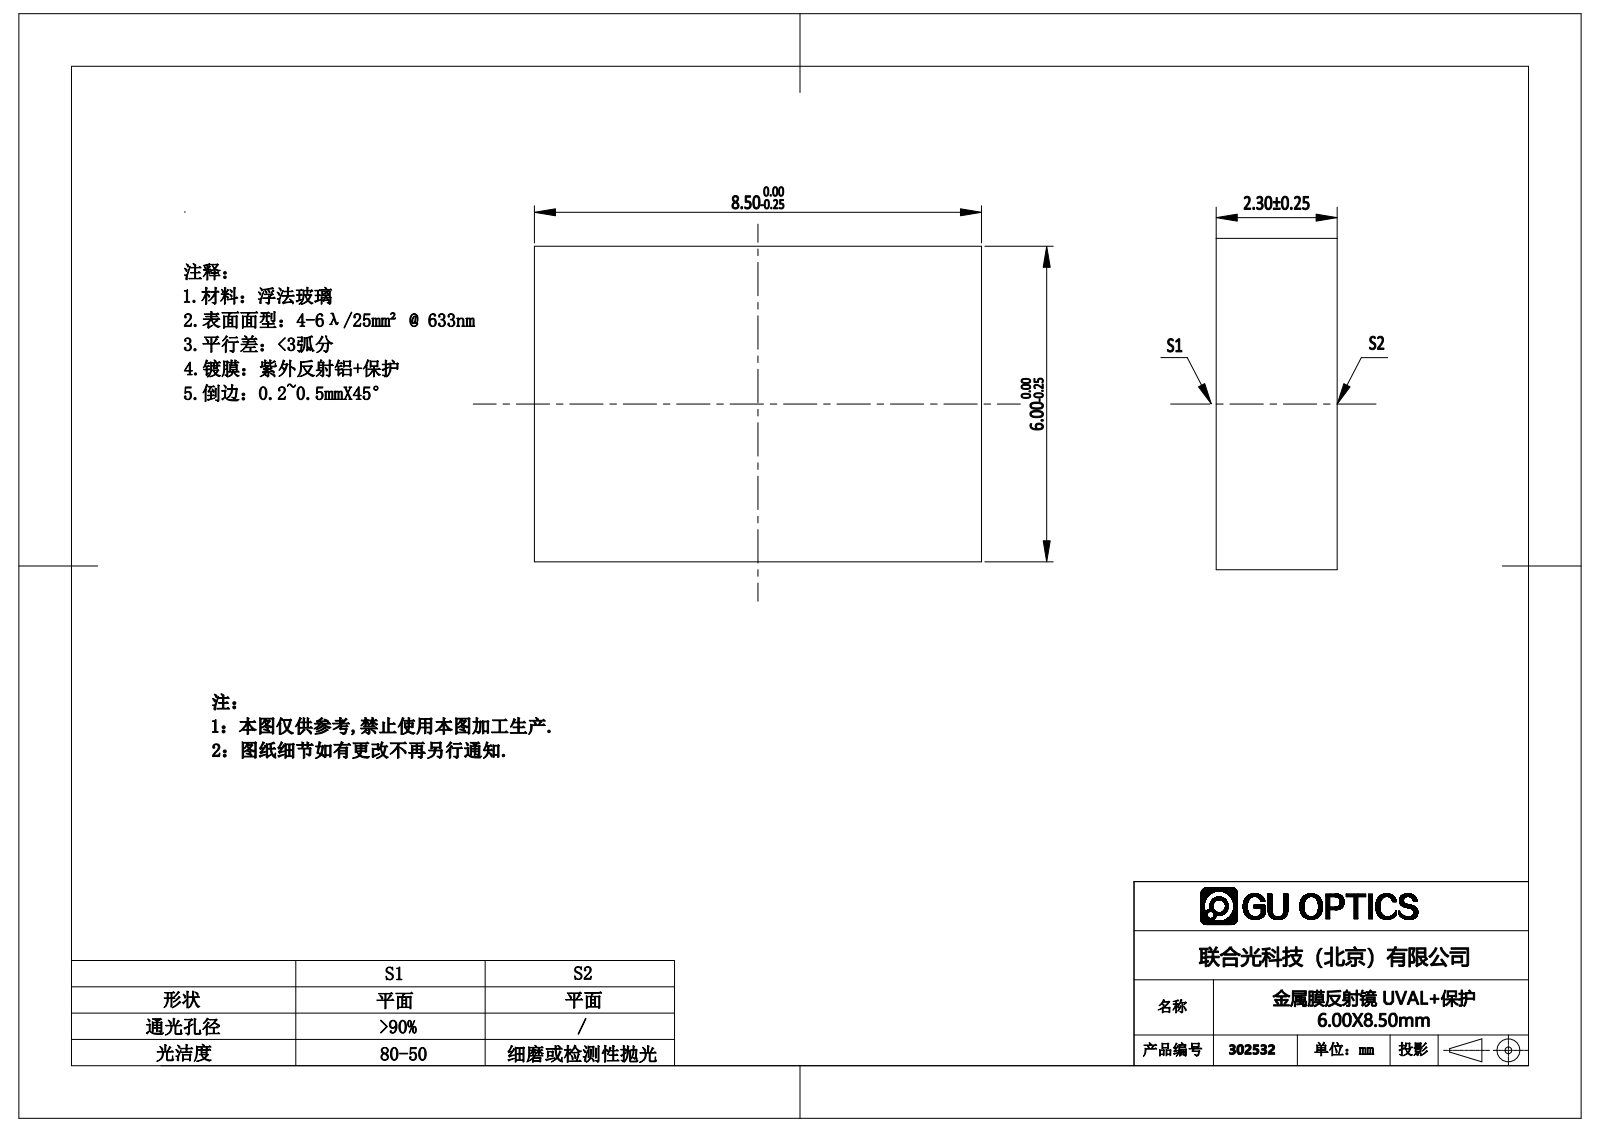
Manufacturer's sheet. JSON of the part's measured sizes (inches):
{"part_name": "302503", "step_written_by": "SolidWorks 2016 (AUTOMOTIVE_DESIGN)", "units": "inches", "bodies": {"solids": 1, "faces": 6, "planar": 6, "cylindrical": 0, "other": 0}, "overall_size": [0.335, 0.236, 0.091], "volume_in3": 0.007, "surface_area_in2": 0.262, "face_to_face_distances": [0.091, 0.236, 0.335]}
